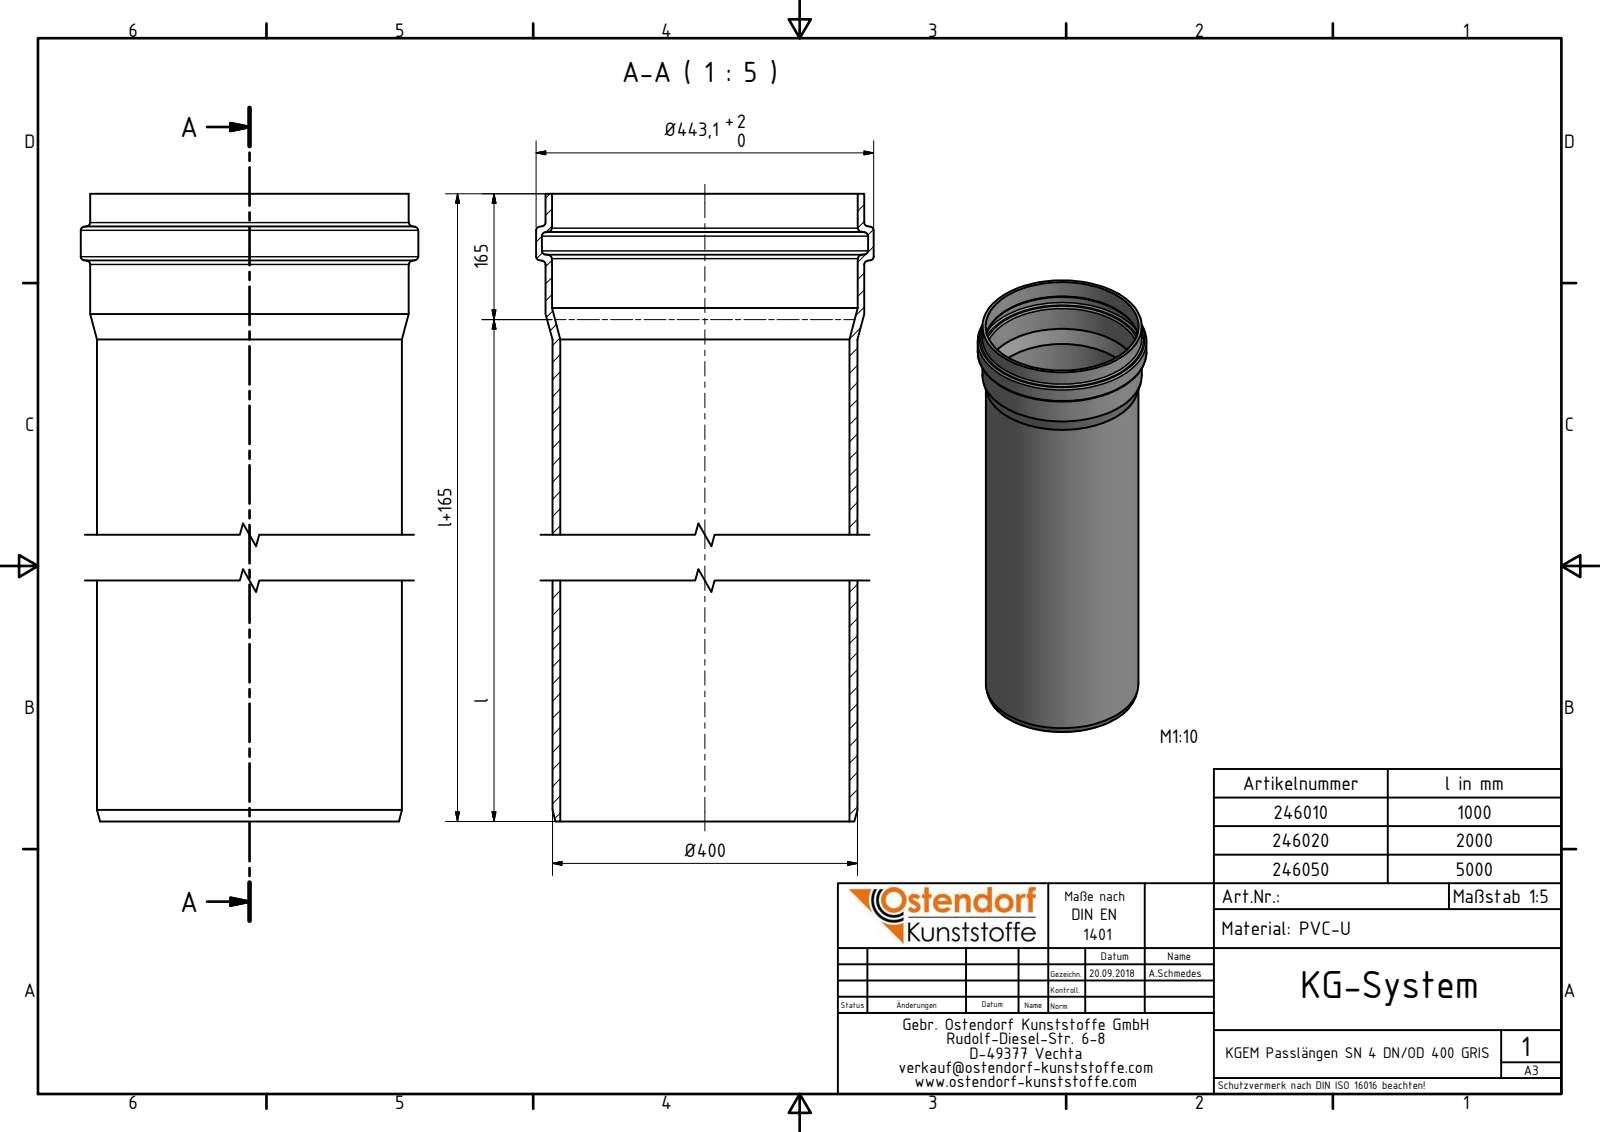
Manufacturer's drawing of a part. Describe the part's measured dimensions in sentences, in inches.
The part is named "246010 KGEM Passlängen SN 4 DN_OD 400x1000 GRIS". Its 3-D file was written by "Autodesk Inventor 2016 (AUTOMOTIVE_DESIGN)". It is 1 solid with 25 faces: 2 planar, 8 cylindrical and 15 other. Overall it measures 45.866 by 17.445 by 17.445 inches. Its volume is 899.5 cubic inches and its surface area 4 569 square inches. Round holes: 1 of diameter 14.943, 1 of diameter 15.811, 1 of diameter 16.862. Round bosses or shafts: 1 of diameter 17.445, 1 of diameter 16.465, 1 of diameter 15.762. The main face-to-face distances are 45.866.
